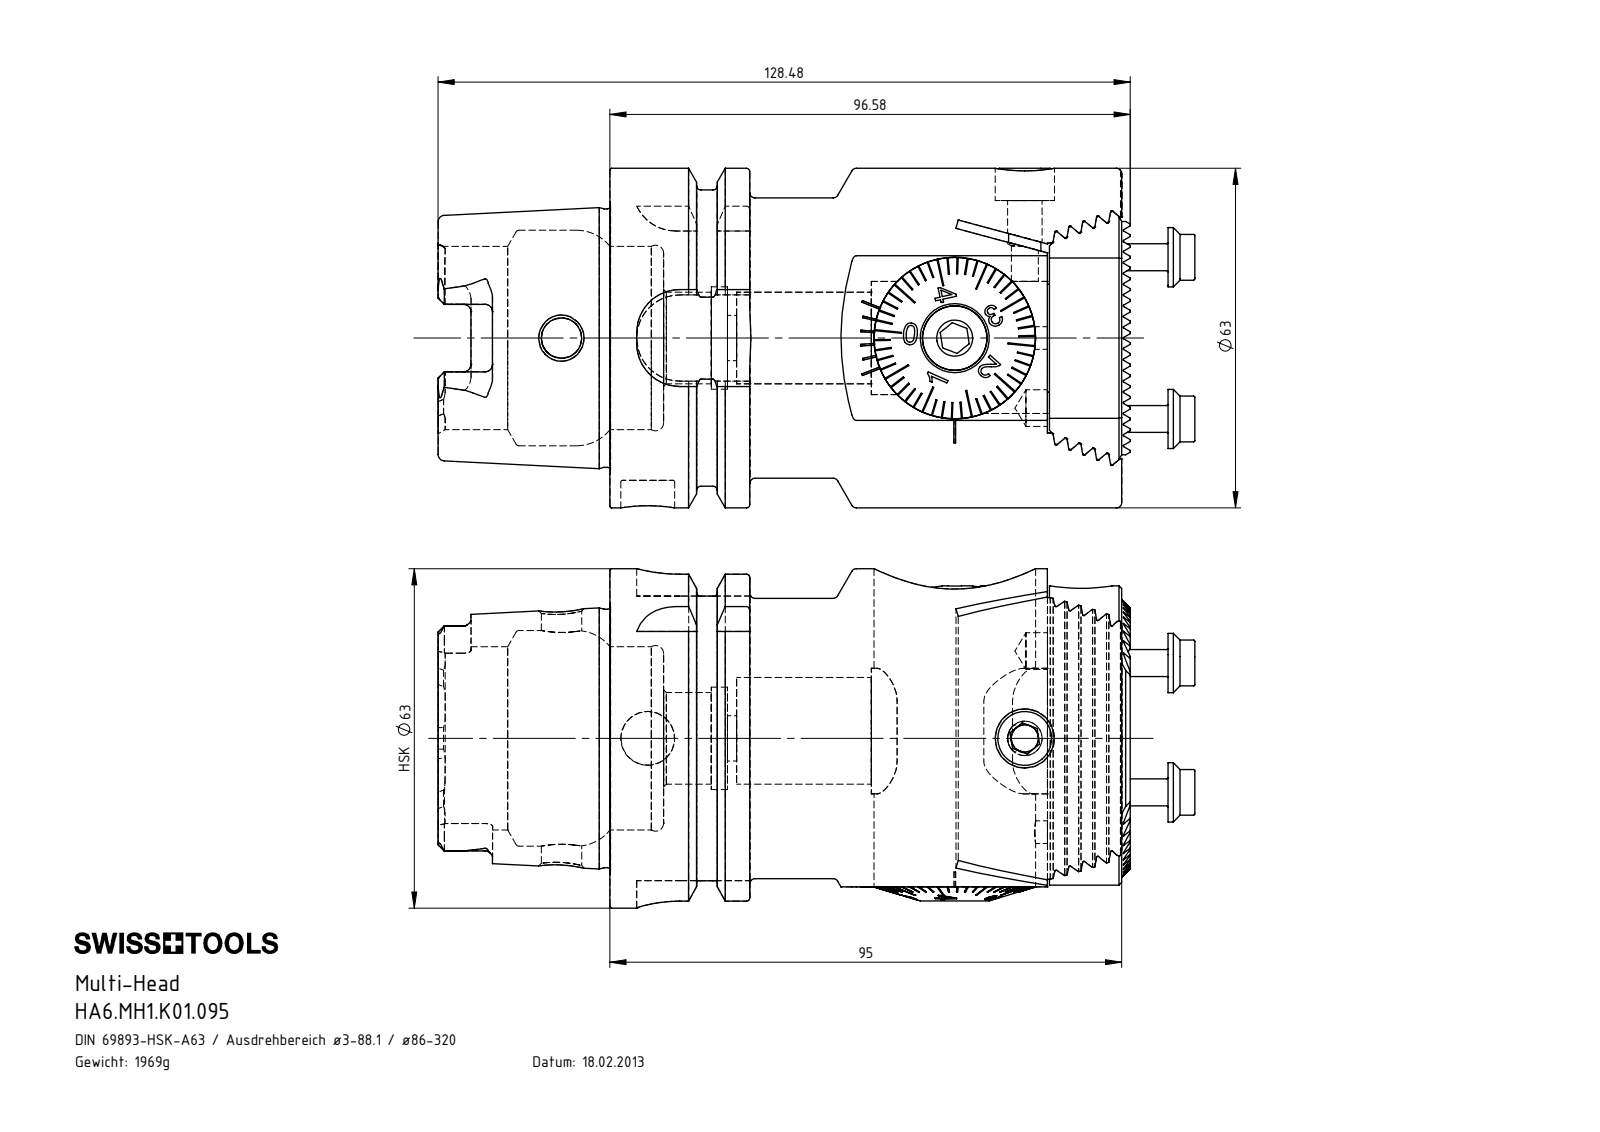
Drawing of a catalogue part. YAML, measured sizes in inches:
part_name: "A55-BG2.012.006_B; HA6-MH1.K00.095_A_Fertigbearbeitung; MH1-BG1.004.049; A55-BG2.013.005_C (+8 more)"
step_written_by: "SolidWorks 2017 (AUTOMOTIVE_DESIGN)"
units: inches
bodies: {solids: 14, faces: 965, planar: 568, cylindrical: 181, other: 216}
overall_size: [5.058, 2.48, 2.48]
volume: 13.84
surface_area: 105.5
round_holes:
  - {diameter: 0.165, count: 5}
  - {diameter: 0.268, count: 3}
  - {diameter: 0.433, count: 3}
  - {diameter: 0.335, count: 2}
  - {diameter: 0.787, count: 2}
  - {diameter: 0.197, count: 1}
  - {diameter: 0.252, count: 1}
  - {diameter: 0.295, count: 1}
  - {diameter: 0.315, count: 1}
  - {diameter: 0.331, count: 1}
  - {diameter: 0.394, count: 1}
  - {diameter: 0.463, count: 1}
round_bosses_or_shafts:
  - {diameter: 0.394, count: 3}
  - {diameter: 2.48, count: 1}
  - {diameter: 2.163, count: 1}
  - {diameter: 2.047, count: 1}
  - {diameter: 1.887, count: 1}
  - {diameter: 1.18, count: 1}
  - {diameter: 1.177, count: 1}
  - {diameter: 0.984, count: 1}
partial_cylinders:
  - {radius: 0.006, count: 21}
  - {radius: 0.008, count: 20}
  - {radius: 0.055, count: 6}
  - {radius: 0.236, count: 6}
  - {radius: 0.113, count: 4}
  - {radius: 0.315, count: 4}
  - {radius: 0.157, count: 2}
  - {radius: 1.22, count: 2}
face_to_face_distances: [0.094, 0.016, 0.187, 0.068, 3.197, 3.213, 0.341, 0.205, 0.528, 3.74]
hole_center_spacings: [0.659, 0.71, 0.808, 0.945, 1.181, 1.37, 1.513, 0.287]
